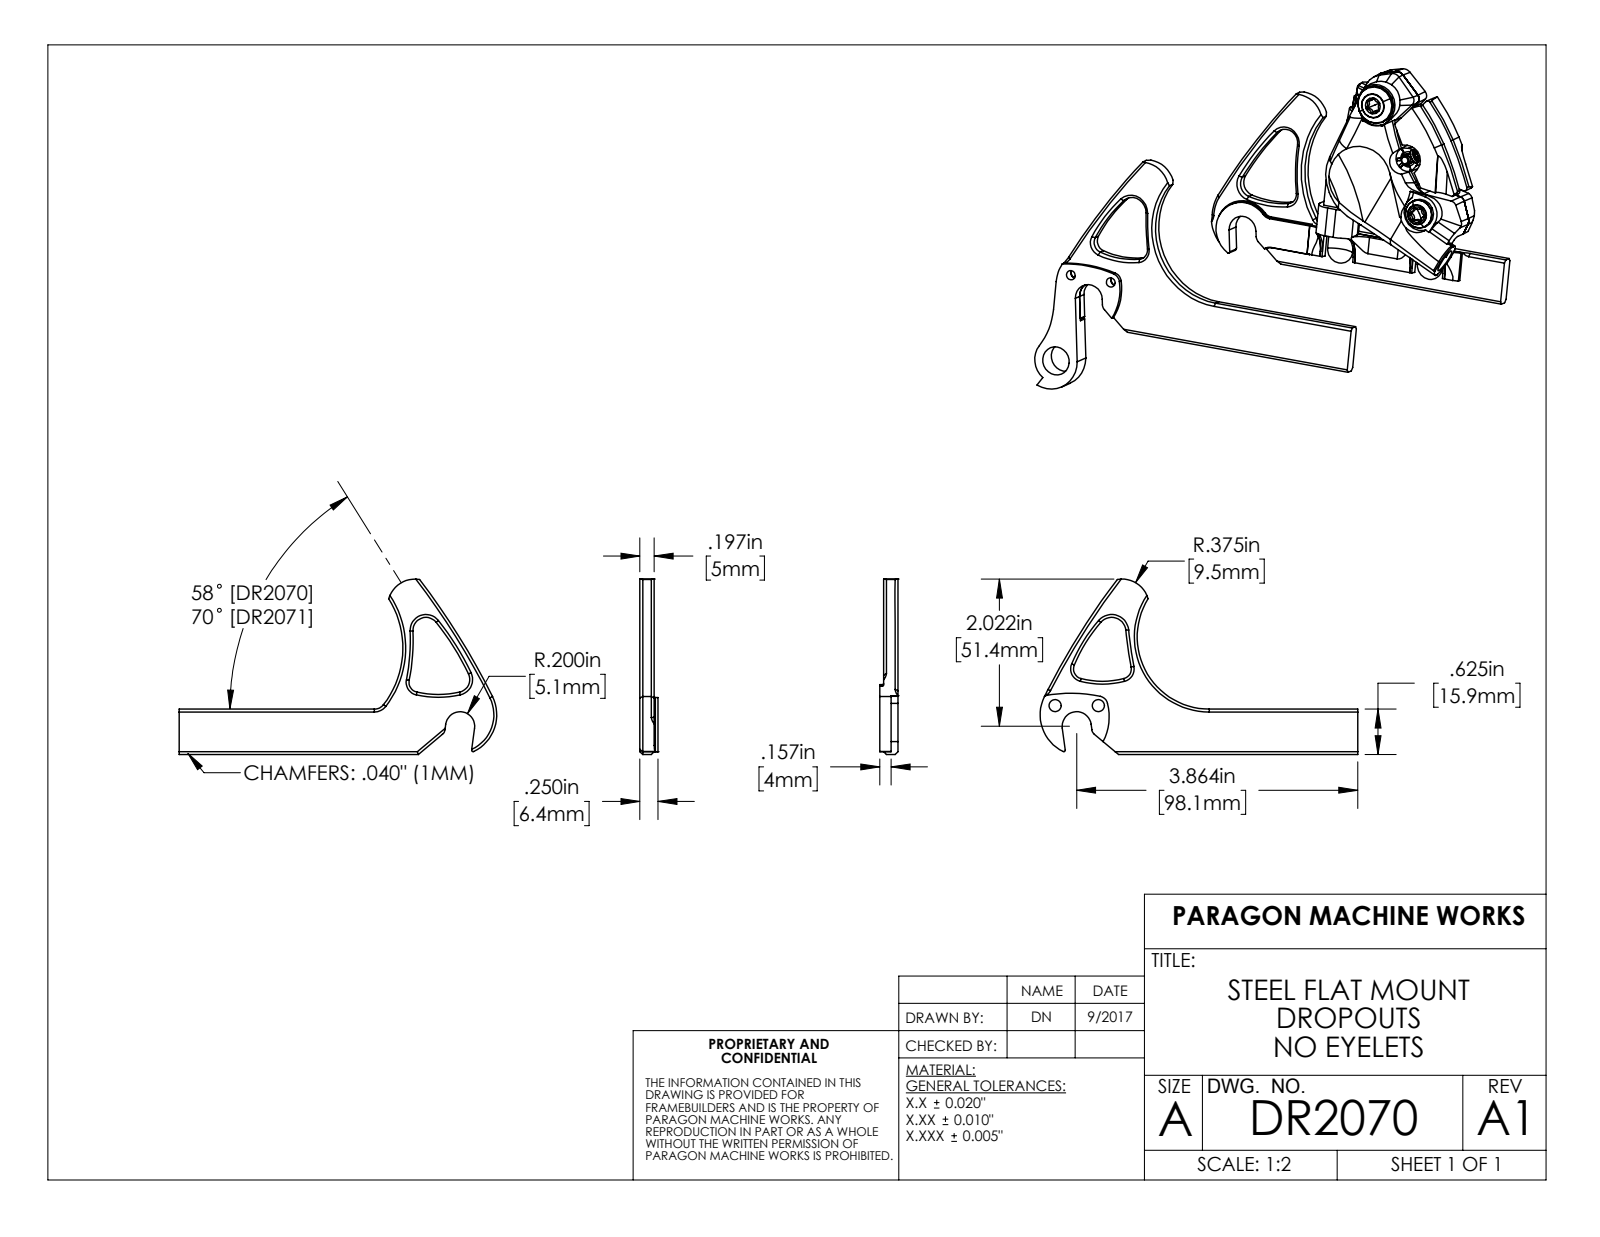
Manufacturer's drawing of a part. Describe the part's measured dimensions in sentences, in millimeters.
The part is named "DR2070; DR2070R; DR2070L; BK2070". Its 3-D file was written by "SolidWorks 2017 (AUTOMOTIVE_DESIGN)". It is 9 solids with 309 faces: 96 planar, 138 cylindrical and 75 other. Overall it measures 173.1 by 110.92 by 61.28 millimeters. Its volume is 31 901 cubic millimeters and its surface area 22 392 square millimeters. Round holes: 2 of diameter 4.22, 2 of diameter 4.5. Round bosses or shafts: 1 of diameter 28.58. Partial cylindrical surfaces (rounded edges, fillets, slot ends): 8 of radius 4.25, 8 of radius 5, 5 of radius 3.5, 4 of radius 1.02, 4 of radius 2.6, 4 of radius 6.35, 3 of radius 0.38, 3 of radius 5.08. The main face-to-face distances are 142.7, 5, 147.7, 137.7, 6.35, 136.35, 4, 141.35, 1.35, 145.35. The hole center spacings are 15.1.
